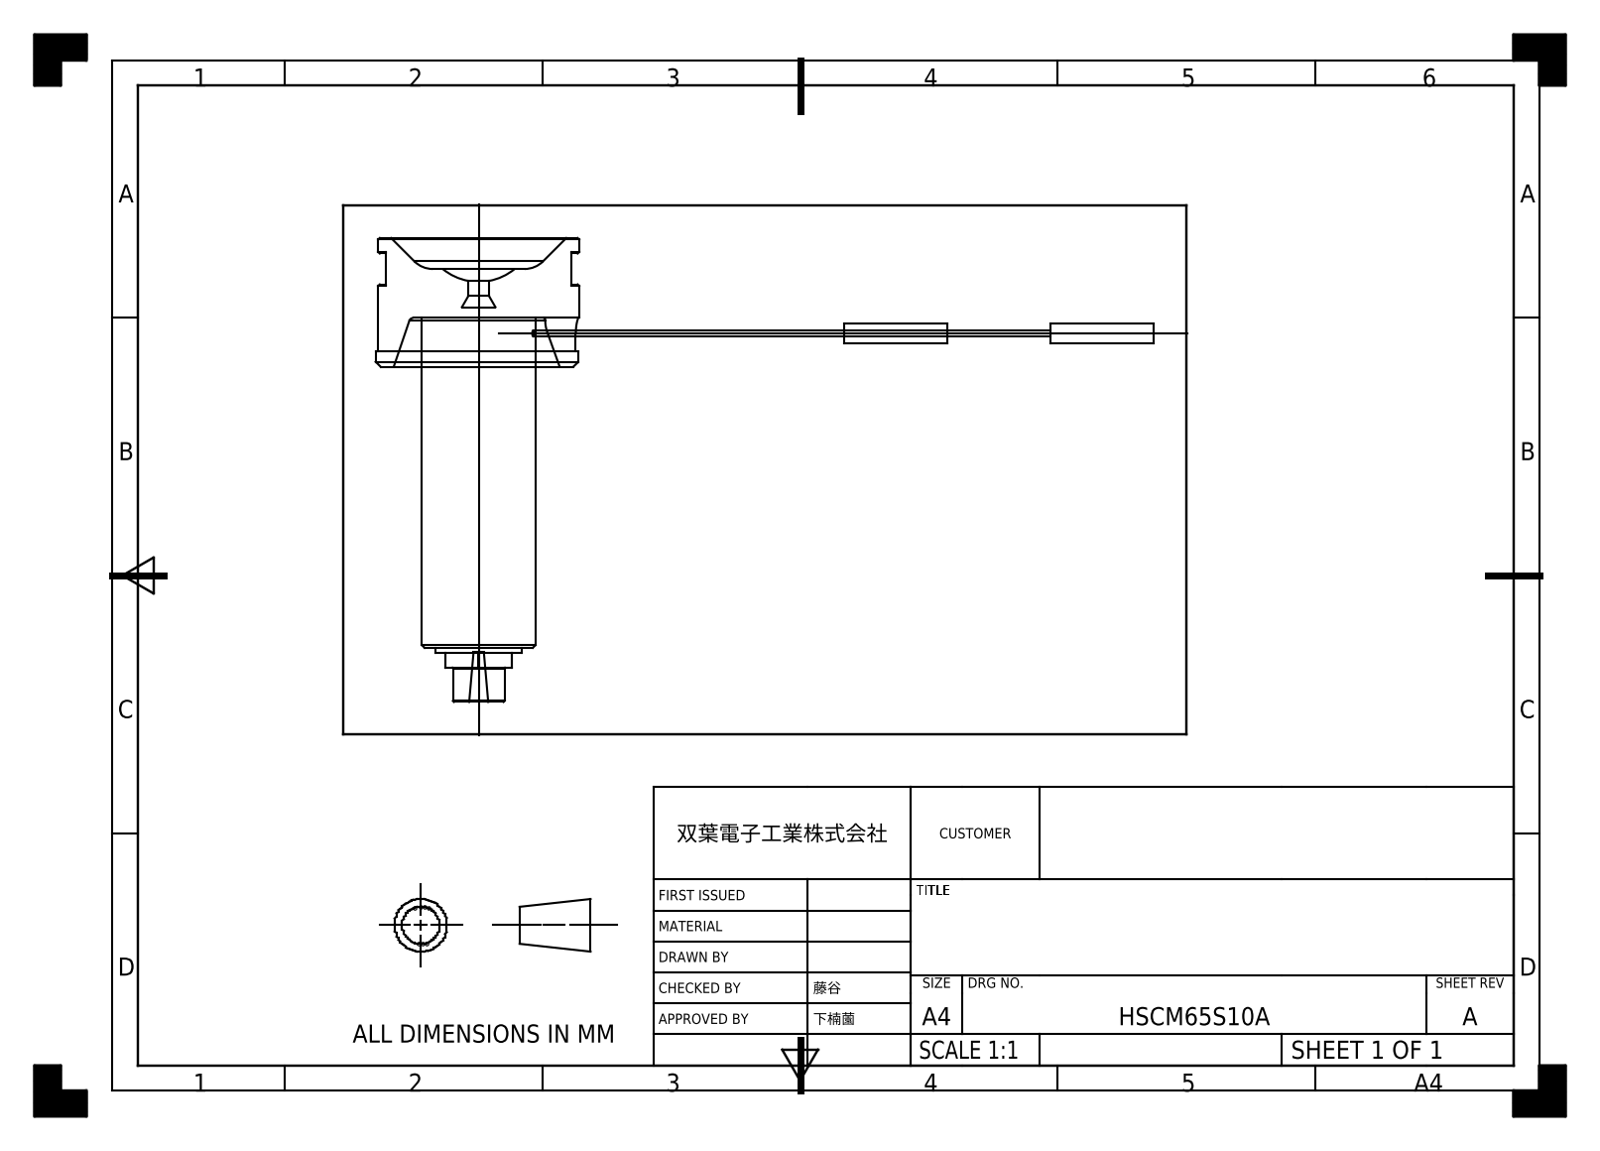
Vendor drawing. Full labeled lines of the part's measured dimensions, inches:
Part name (STEP PRODUCT): HSCM65S10A
STEP written by: SIEMENS PLM Software NX 2023 (AUTOMOTIVE_DESIGN)
Units: inches
Bodies: 1 solid, 63 faces (29 planar, 18 cylindrical, 16 other)
Overall size (bounding box): 5.945 × 3.543 × 1.575
Volume: 2.736 in³ · Surface area: 19.24 in²
Round holes (diameter × count): ⌀0.157 ×1
Round bosses / shafts (diameter × count): ⌀0.157 ×2, ⌀0.047 ×2, ⌀1.575 ×1, ⌀1.535 ×1, ⌀0.866 ×1, ⌀0.665 ×1, ⌀0.394 ×1
Partial cylindrical surfaces — rounded edges, fillets, slot ends (radius × count): R0.118 ×2, R0.293 ×1
Main face-to-face distances: 0.374, 0.984, 0.61, 2.933, 2.559, 3.13, 2.52, 2.146, 0.118, 0.236
